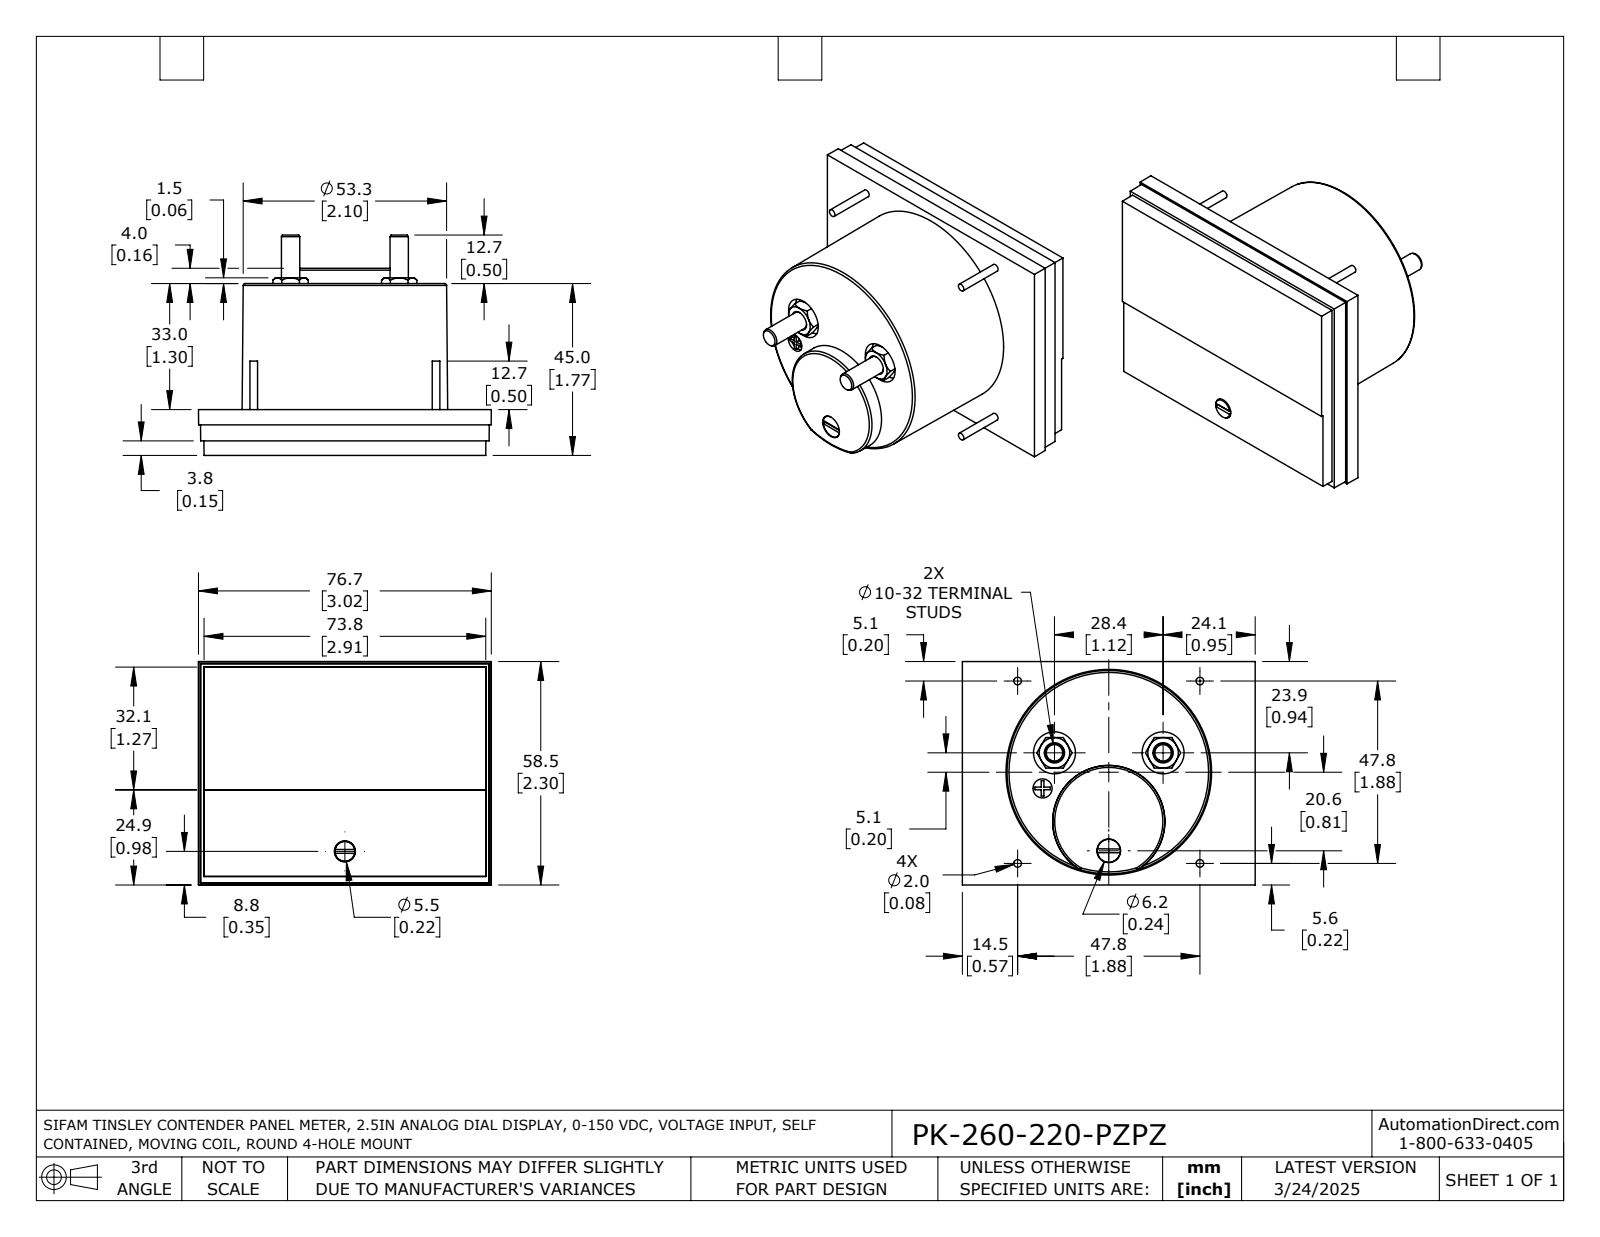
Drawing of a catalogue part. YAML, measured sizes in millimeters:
part_name: "PK-260-220-PZPZ"
step_written_by: "SolidWorks 2021 (AUTOMOTIVE_DESIGN)"
units: millimeters
bodies: {solids: 1, faces: 192, planar: 95, cylindrical: 37, other: 60}
overall_size: [76.7, 58.5, 57.7]
volume: 125500
surface_area: 23580
round_holes:
  - {diameter: 5, count: 3}
  - {diameter: 11, count: 2}
  - {diameter: 5.3, count: 1}
  - {diameter: 5.5, count: 1}
  - {diameter: 6.2, count: 1}
round_bosses_or_shafts:
  - {diameter: 2, count: 4}
  - {diameter: 4.8, count: 2}
  - {diameter: 6, count: 1}
  - {diameter: 5.2, count: 1}
partial_cylinders:
  - {radius: 0.8, count: 1}
face_to_face_distances: [0.5, 12, 3.3, 8.2, 3.8, 11.5, 1.4, 2, 10.1, 1.9]
hole_center_spacings: [29.3, 29.5, 9.8, 23.8, 23.9, 28.4, 32.9]
